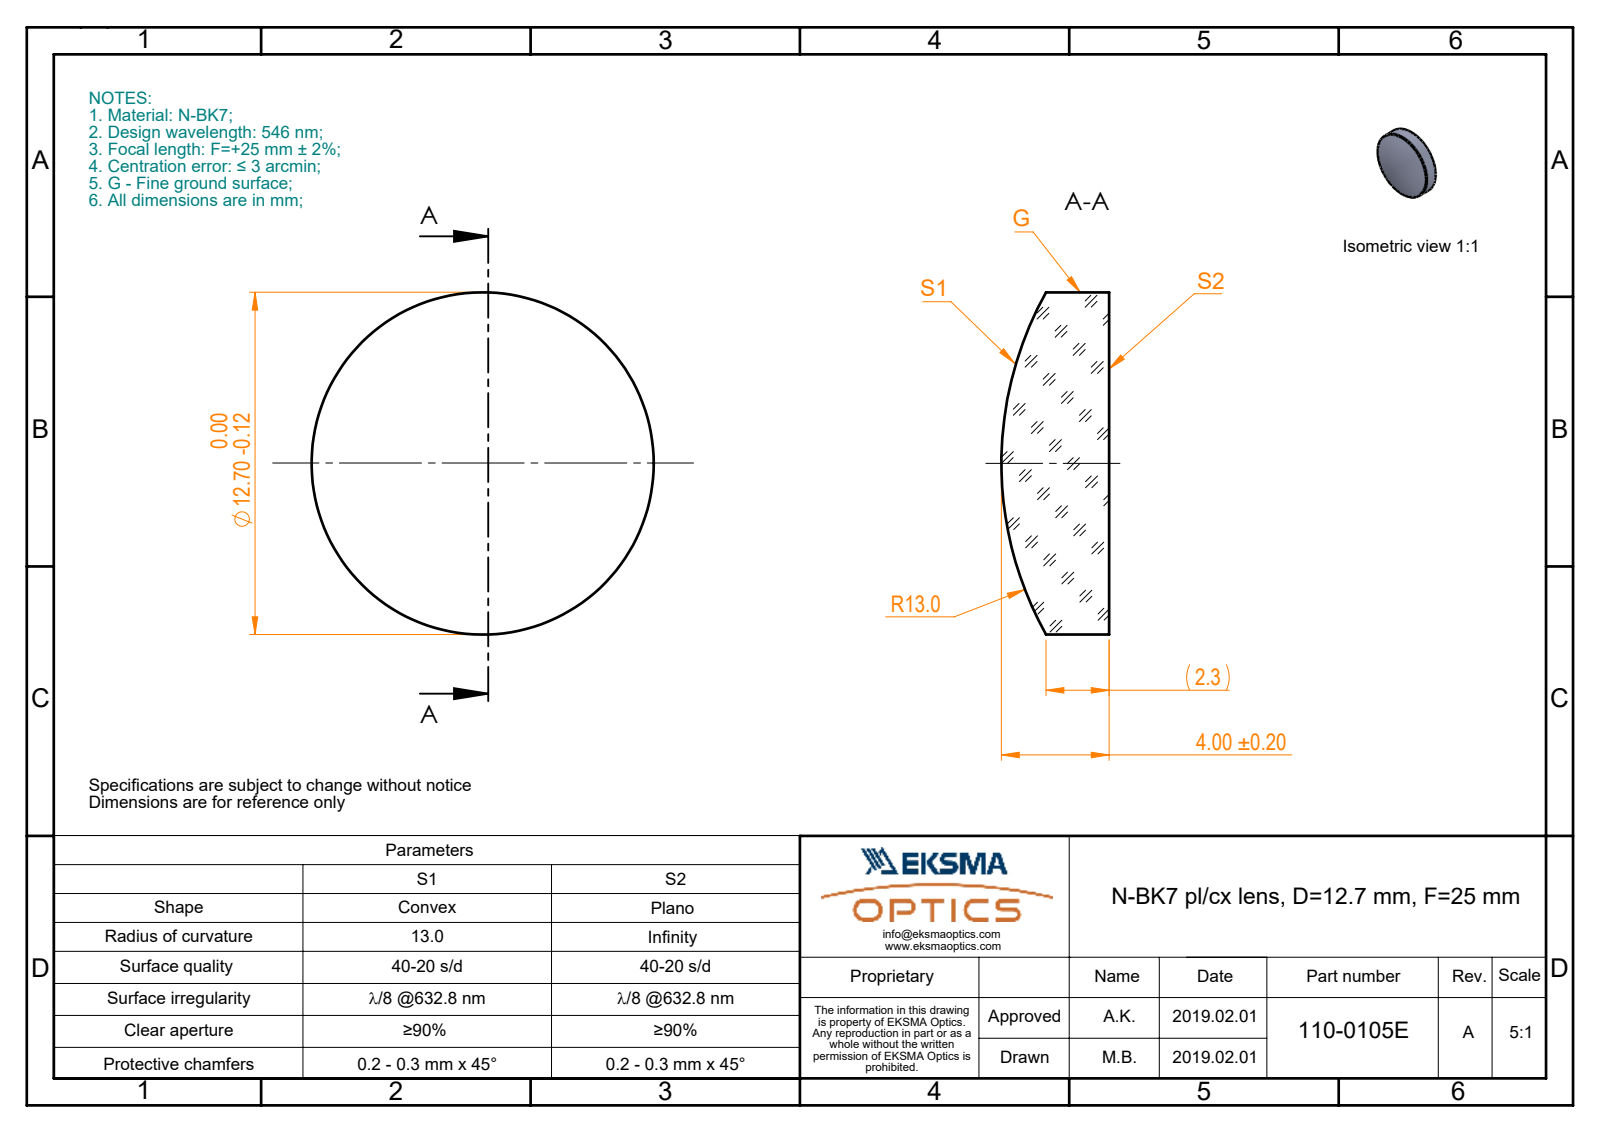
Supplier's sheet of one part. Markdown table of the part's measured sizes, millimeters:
| quantity | value |
| --- | --- |
| part name | 110-0105E BK7 pl-cx 12.7 F25 |
| STEP written by | SolidWorks 2017 (CONFIG_CONTROL_DESIGN) |
| units | millimeters |
| bodies | 1 solid, 5 faces (1 planar, 2 cylindrical, 2 other) |
| overall size | 12.7 × 12.7 × 4 |
| volume | 404 mm³ |
| surface area | 355 mm² |
| round bosses / shafts (diameter × count) | 12.7 × 1 |
